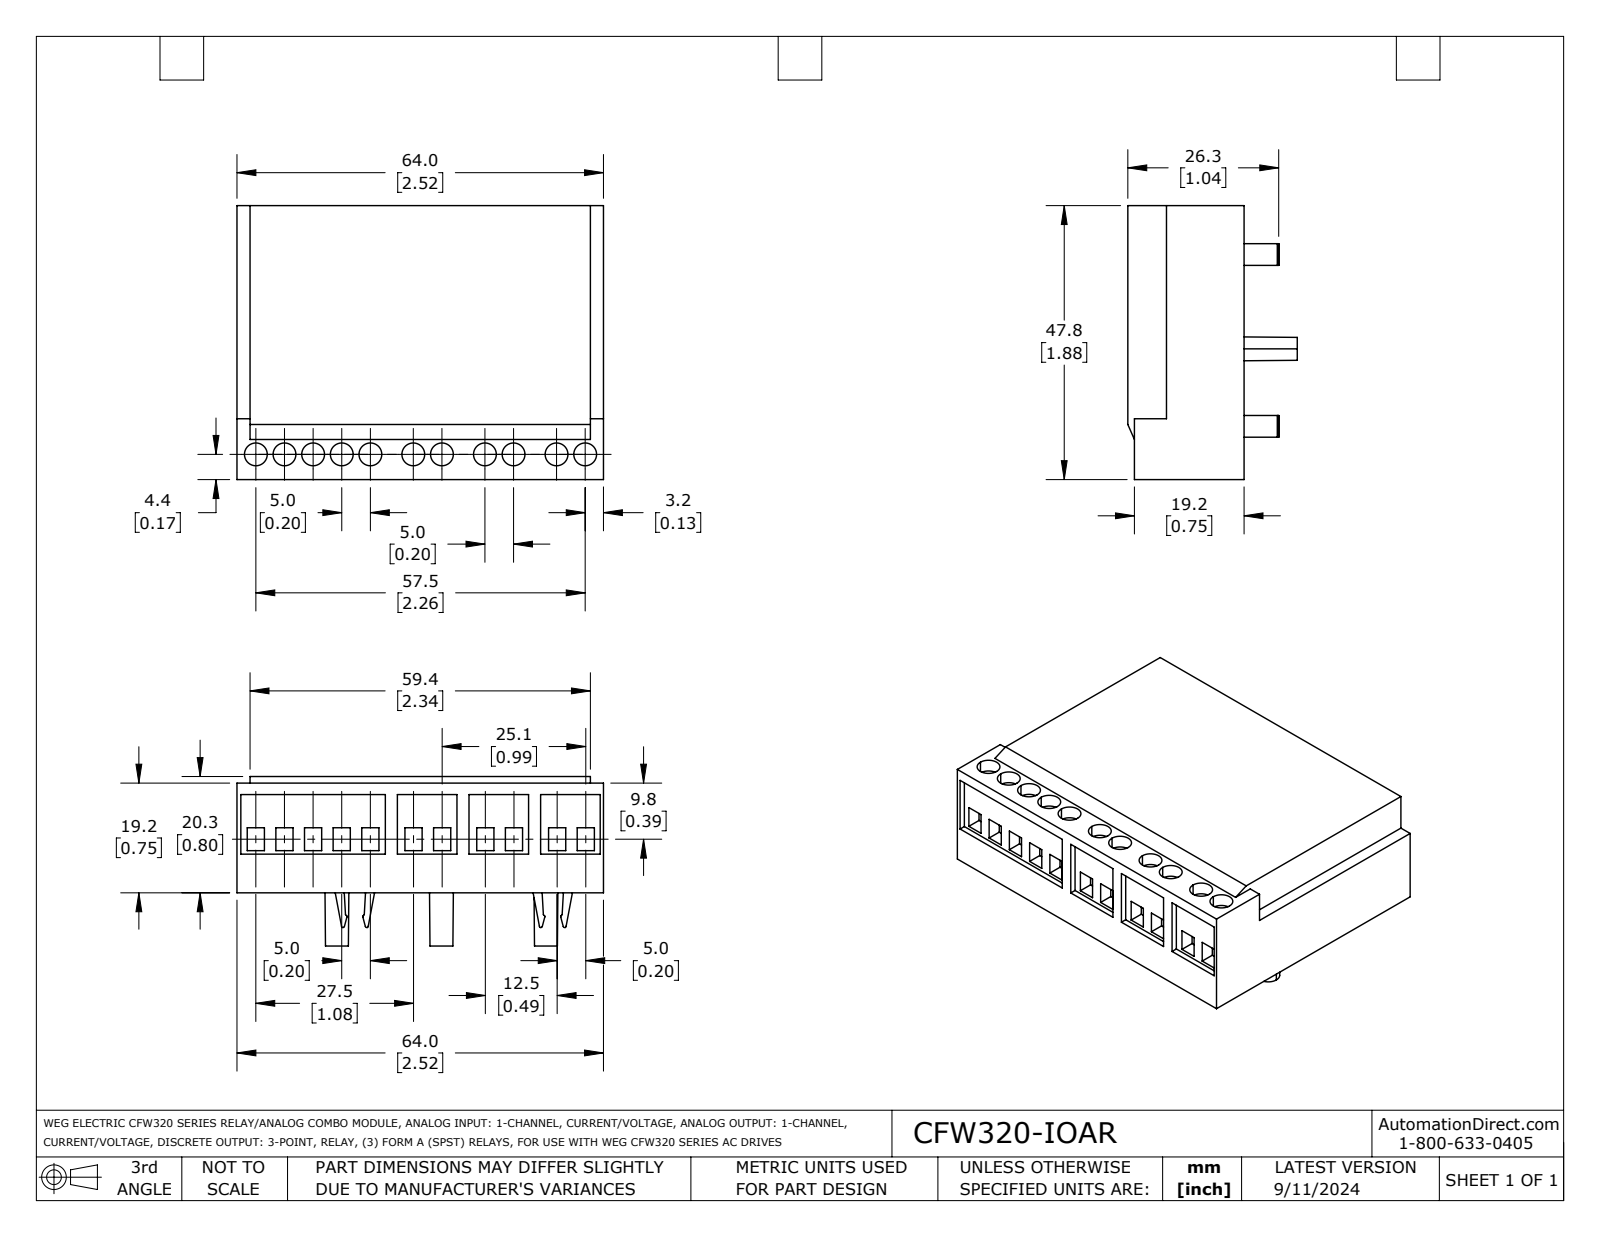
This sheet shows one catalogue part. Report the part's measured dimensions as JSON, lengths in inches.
{"part_name": "CFW320 IOAR", "step_written_by": "SolidWorks 2021 (AUTOMOTIVE_DESIGN)", "units": "inches", "bodies": {"solids": 1, "faces": 206, "planar": 162, "cylindrical": 22, "other": 22}, "overall_size": [2.52, 1.883, 1.165], "volume_in3": 3.553, "surface_area_in2": 19.05, "round_holes": [[0.157, 11]], "face_to_face_distances": [0.799, 1.883, 2.52, 0.09, 2.43, 0.042, 1.841, 0.165, 0.634, 0.754], "hole_center_spacings": [0.197, 0.493, 0.394, 0.296, 0.492, 0.591, 0.689, 0.689]}
